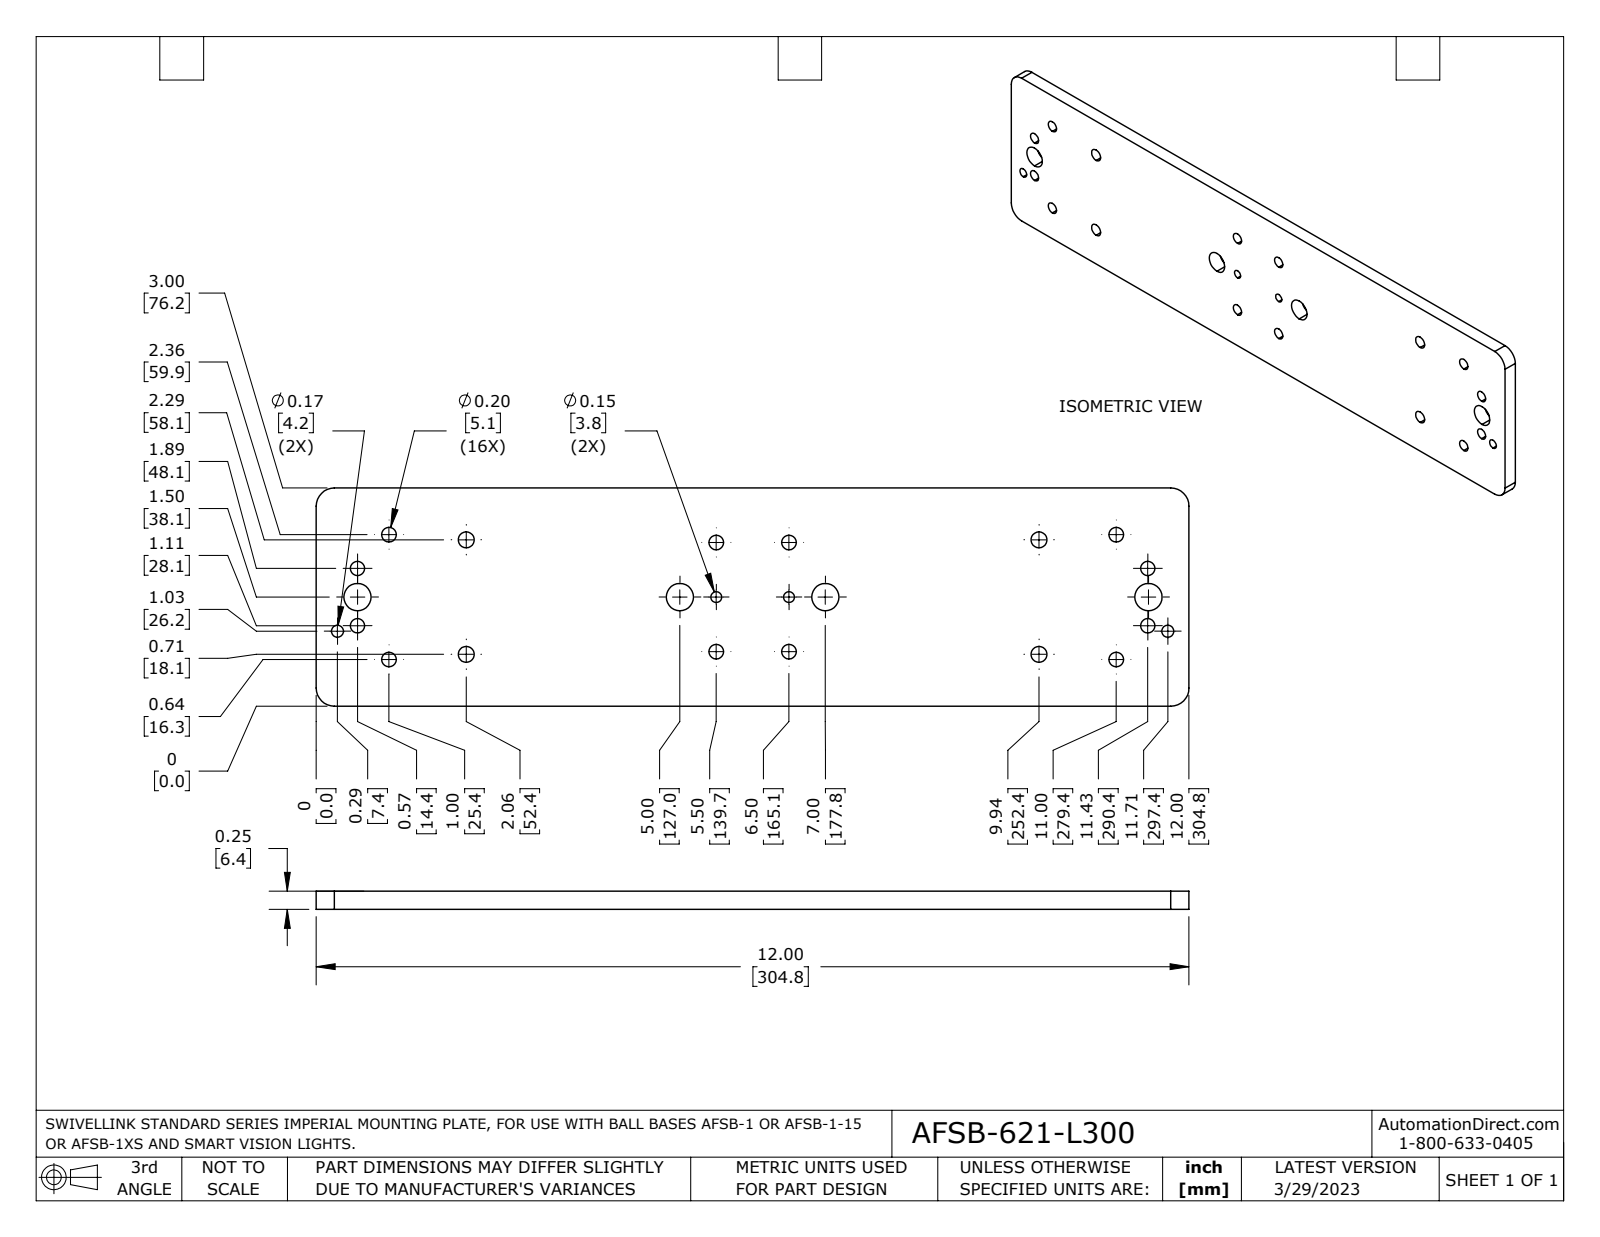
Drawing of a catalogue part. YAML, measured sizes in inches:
part_name: "AFSB-621-L300"
step_written_by: "SolidWorks 2021 (AUTOMOTIVE_DESIGN)"
units: inches
bodies: {solids: 1, faces: 58, planar: 6, cylindrical: 52, other: 0}
overall_size: [12, 3, 0.25]
volume: 8.725
surface_area: 81.44
round_holes:
  - {diameter: 0.201, count: 8}
  - {diameter: 0.197, count: 4}
  - {diameter: 0.219, count: 4}
  - {diameter: 0.375, count: 4}
  - {diameter: 0.15, count: 2}
  - {diameter: 0.165, count: 2}
partial_cylinders:
  - {radius: 0.25, count: 4}
face_to_face_distances: [0.25, 3, 12]
hole_center_spacings: [0.394, 0.635, 0.75, 0.902, 1.064, 1.25, 1.324, 1.5]
